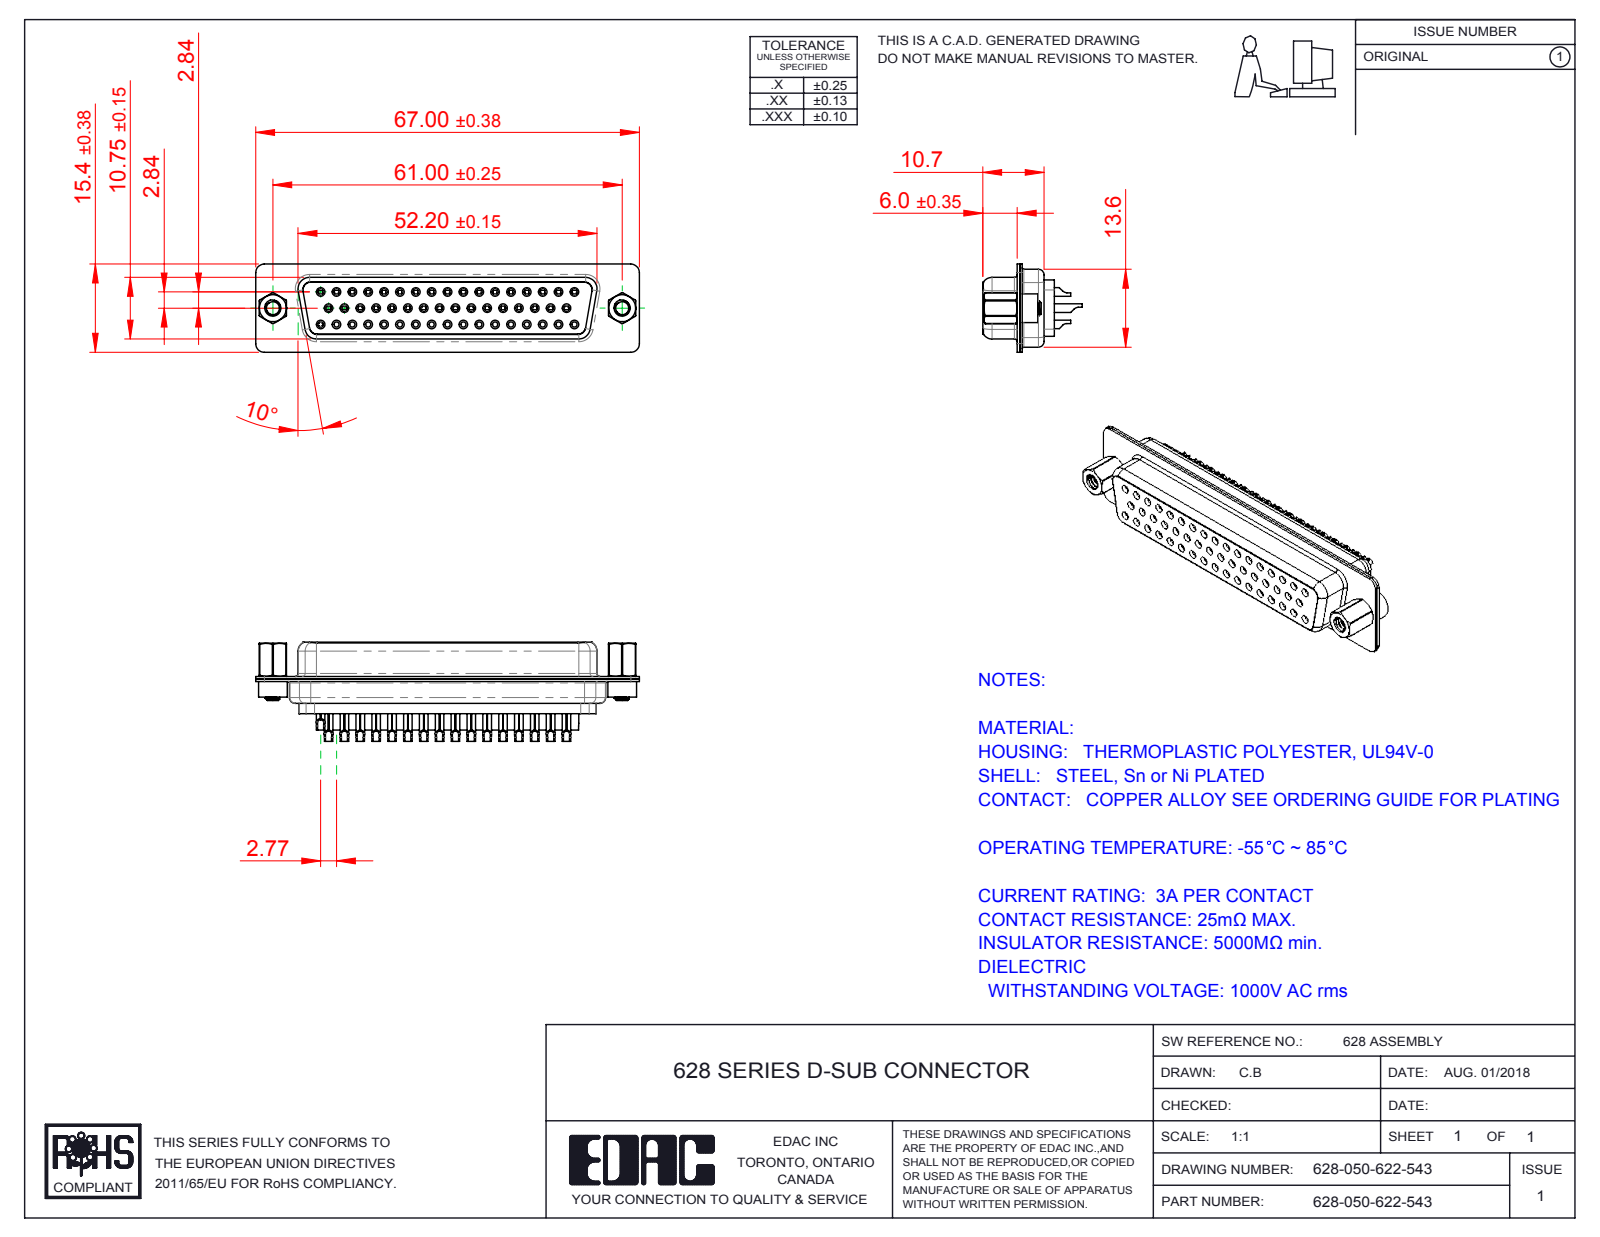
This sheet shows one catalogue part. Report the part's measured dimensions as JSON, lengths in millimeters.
{"part_name": "628 Shell Front_50 Contacts; 628 Housing_50 LP; 628 Contact Row 3_22L; 628-050-622-543 (+5 more)", "step_written_by": "SolidWorks 2016 (CONFIG_CONTROL_DESIGN)", "units": "millimeters", "bodies": {"solids": 41, "faces": 3639, "planar": 851, "cylindrical": 1187, "other": 1601}, "overall_size": [67, 17.35, 15.4], "volume_mm3": 6848, "surface_area_mm2": 14615, "round_holes": [[0.9, 50], [1.6, 50], [0.8, 34], [1.1, 34], [1.7, 17], [1.5, 16], [2, 16], [2.26, 2], [2.29, 2], [4, 2], [4.8, 2]], "round_bosses_or_shafts": [[2, 34], [1.5, 34], [1.2, 34], [5, 2], [4.9, 2], [2.79, 2]], "partial_cylinders_radius": [[0.28, 33], [1.5, 16], [2, 12], [1.35, 8], [1, 7], [0.25, 4], [0.5, 4], [0.6, 4]], "face_to_face_distances": [0.45, 0.4, 10.3, 0.9, 6.05, 6.5, 12.5, 6.45, 6, 11.33], "hole_center_spacings": [3.16, 2.77, 5.54, 8.31, 11.08, 13.85, 16.62, 19.39]}
